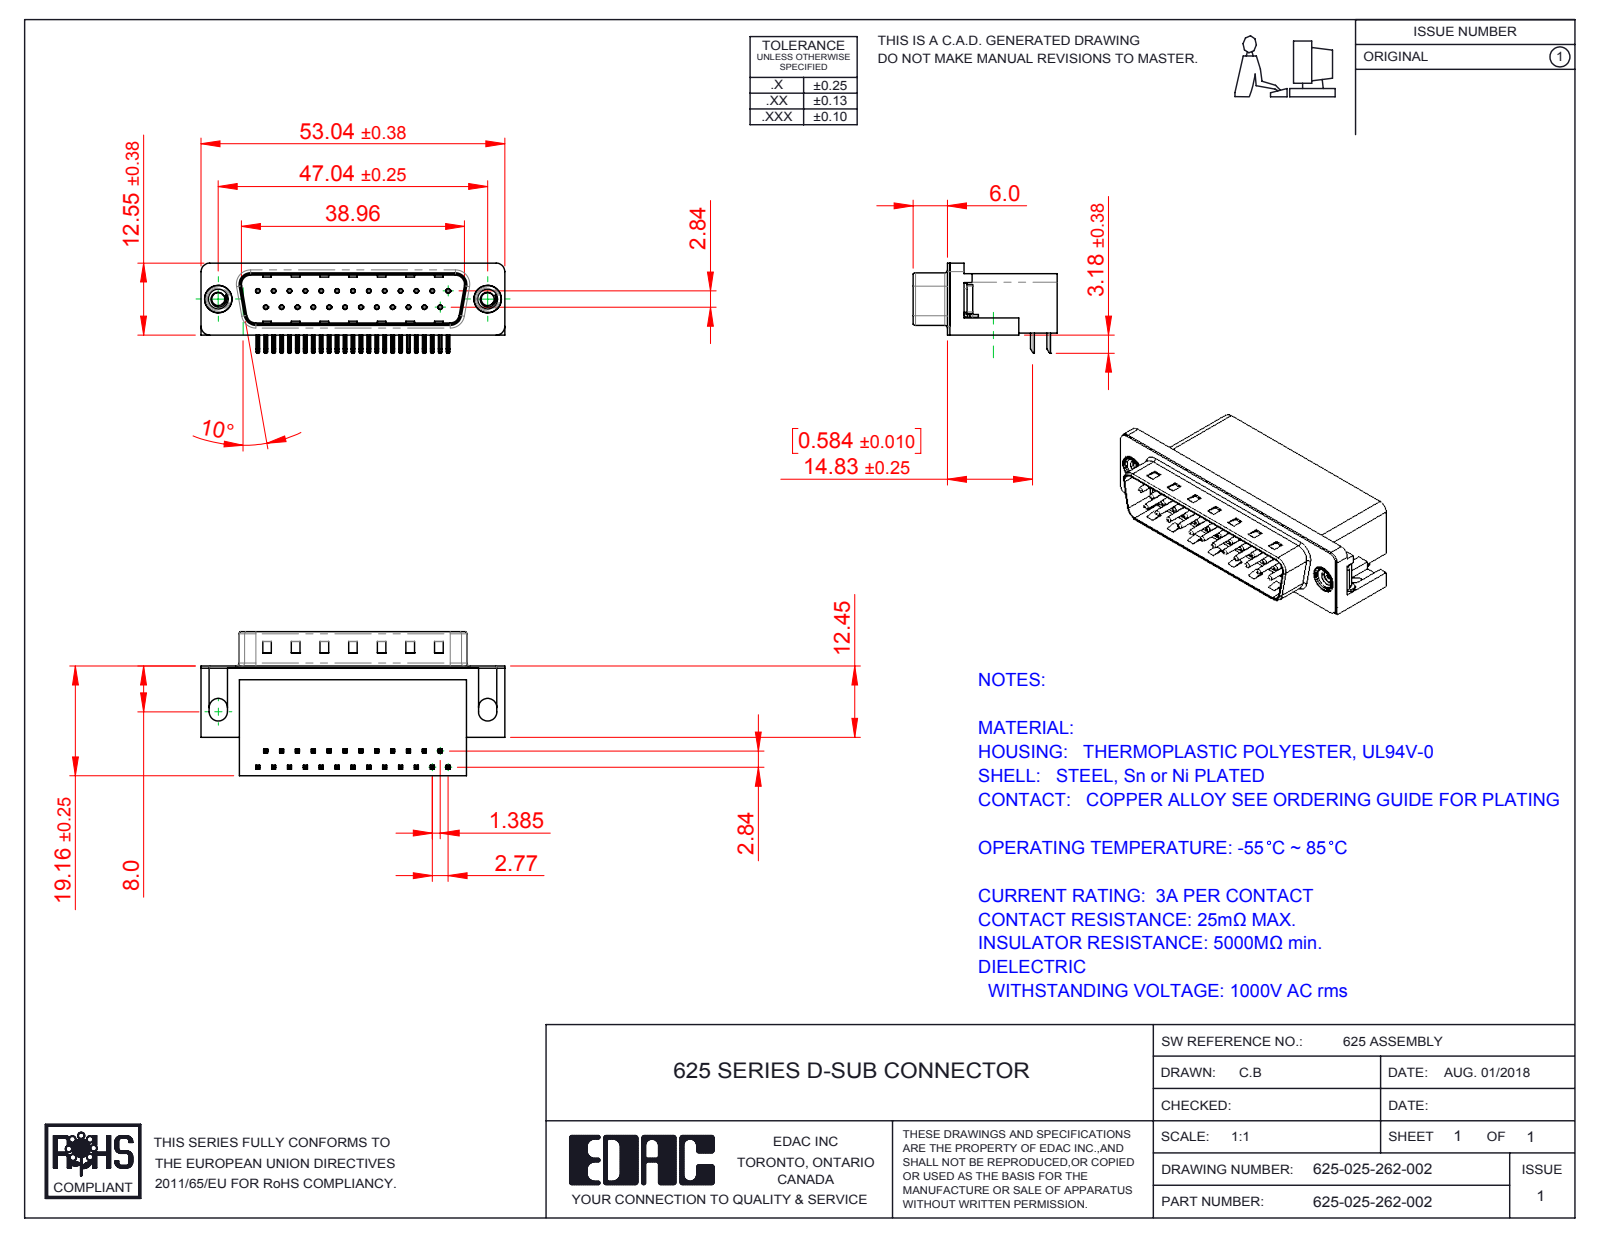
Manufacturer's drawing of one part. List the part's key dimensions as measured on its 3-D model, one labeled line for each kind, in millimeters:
Part name (STEP PRODUCT): 625 Contact Bottom; 625 Shell_25 Socket; 625 Housing_25 Socket; 625 Contact Top (+3 more)
STEP written by: SolidWorks 2016 (CONFIG_CONTROL_DESIGN)
Units: millimetres
Bodies: 31 solids, 2263 faces (1407 planar, 657 cylindrical, 199 other)
Overall size (bounding box): 53.04 × 25.16 × 15.73
Volume: 9 138 mm³ · Surface area: 8 728 mm²
Round holes (diameter × count): ⌀0.35 ×25, ⌀0.8 ×25, ⌀2.26 ×2, ⌀4 ×2, ⌀4.8 ×2, ⌀5 ×2
Round bosses / shafts (diameter × count): ⌀0.75 ×25, ⌀4.9 ×2, ⌀4.75 ×2, ⌀3.9 ×2
Partial cylindrical surfaces — rounded edges, fillets, slot ends (radius × count): R0.25 ×108, R0.12 ×50, R1 ×16, R0.5 ×9, R1.6 ×8, R1.5 ×7, R0.9 ×4, R2 ×4
Main face-to-face distances: 0.4, 10.35, 18.76, 2.1, 8.76, 10.46, 10.86, 1.7, 19.16, 10.11
Hole centre spacings: 3.16, 2.77, 11.08, 5.54, 8.31, 5.03, 13.85, 7.48
